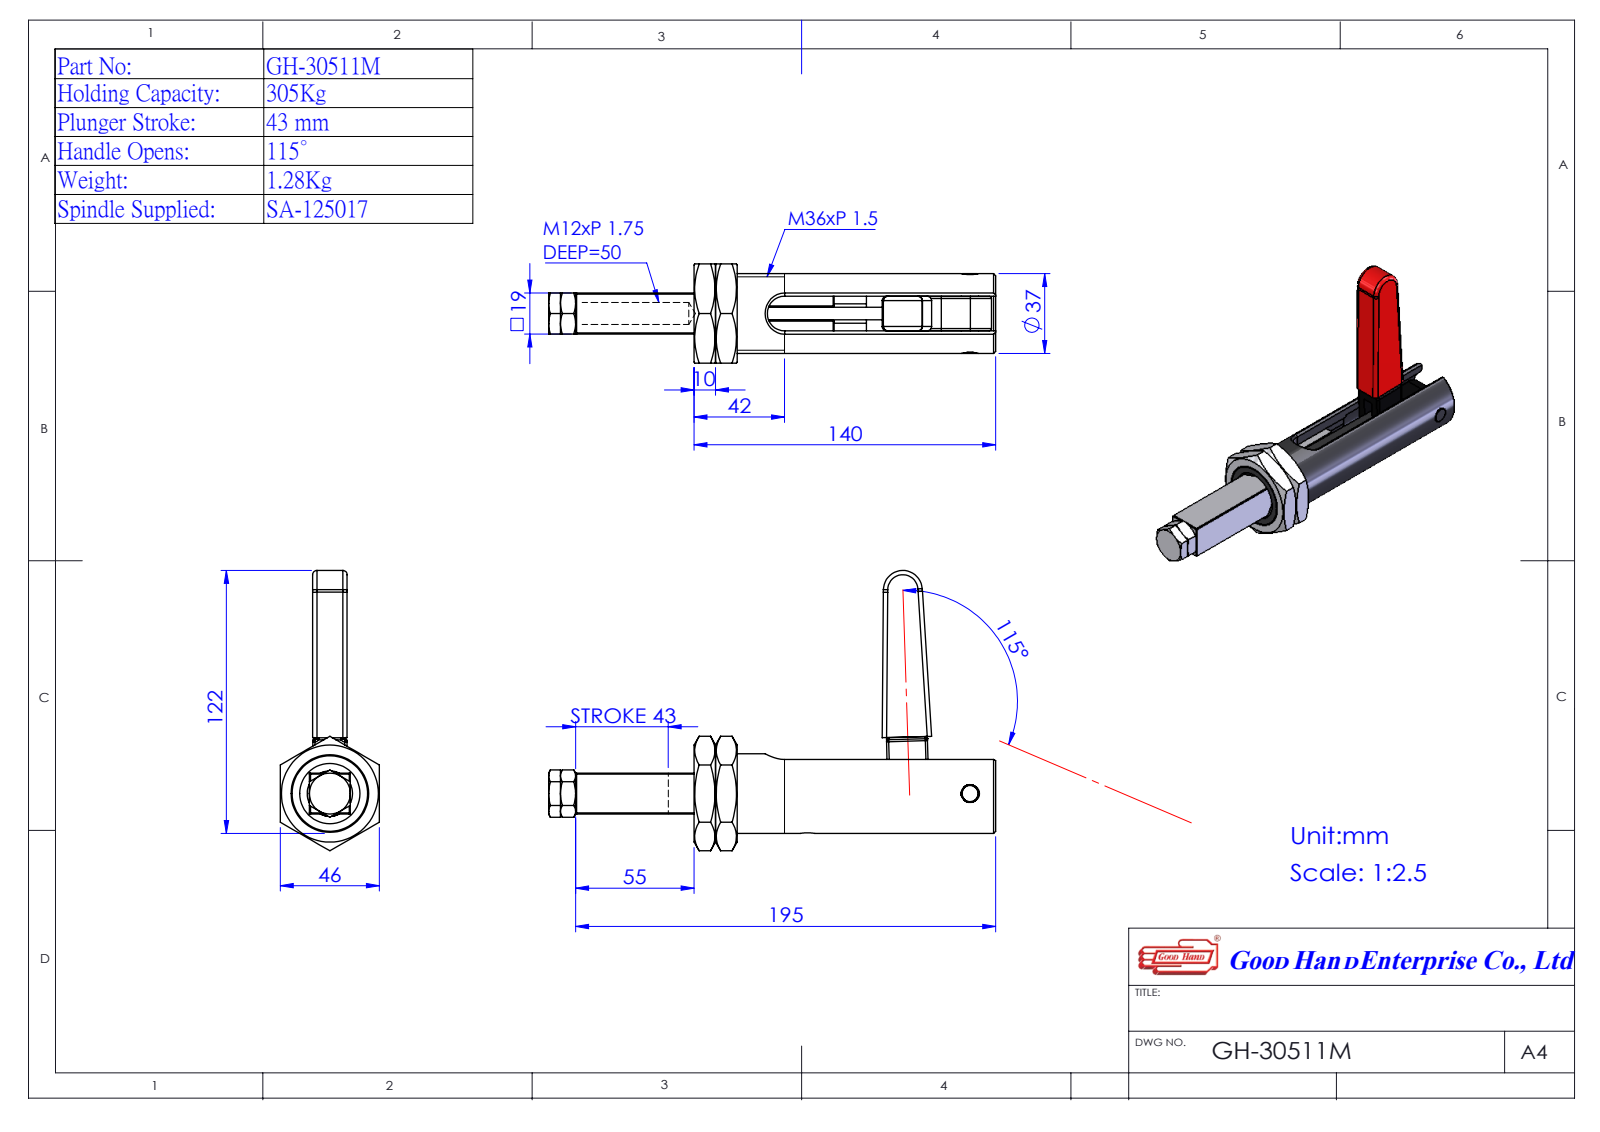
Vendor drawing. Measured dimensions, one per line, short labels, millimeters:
name: Group3^GH-30511M(簡化)-1; GH-30511M(簡化)-1; 430510MB05-2^GH-30511M(簡化)-1; Group1^GH-30511M(簡化) (+2 more)
written by: SolidWorks 2016 (AUTOMOTIVE_DESIGN)
unit: mm
bodies: 5 solids, 233 faces (89 planar, 86 cylindrical, 58 other)
size: 209.51 × 131.11 × 46
volume: 167 430 mm³; area: 64 148 mm²
holes: 3× ⌀6, 1× ⌀5.5, 1× ⌀10.2, 1× ⌀27
bosses: 1× ⌀37, 1× ⌀36, 1× ⌀18, 1× ⌀12, 1× ⌀3
rounds: 4× R0.8, 4× R2.2, 3× R9.5, 2× R6, 1× R8.05, 1× R8.2, 1× R11.17
face distances: 18.61, 5, 6, 6.3, 12.3, 16, 11.05, 11, 12.31, 6.31
hole spacings: 28, 70, 98
